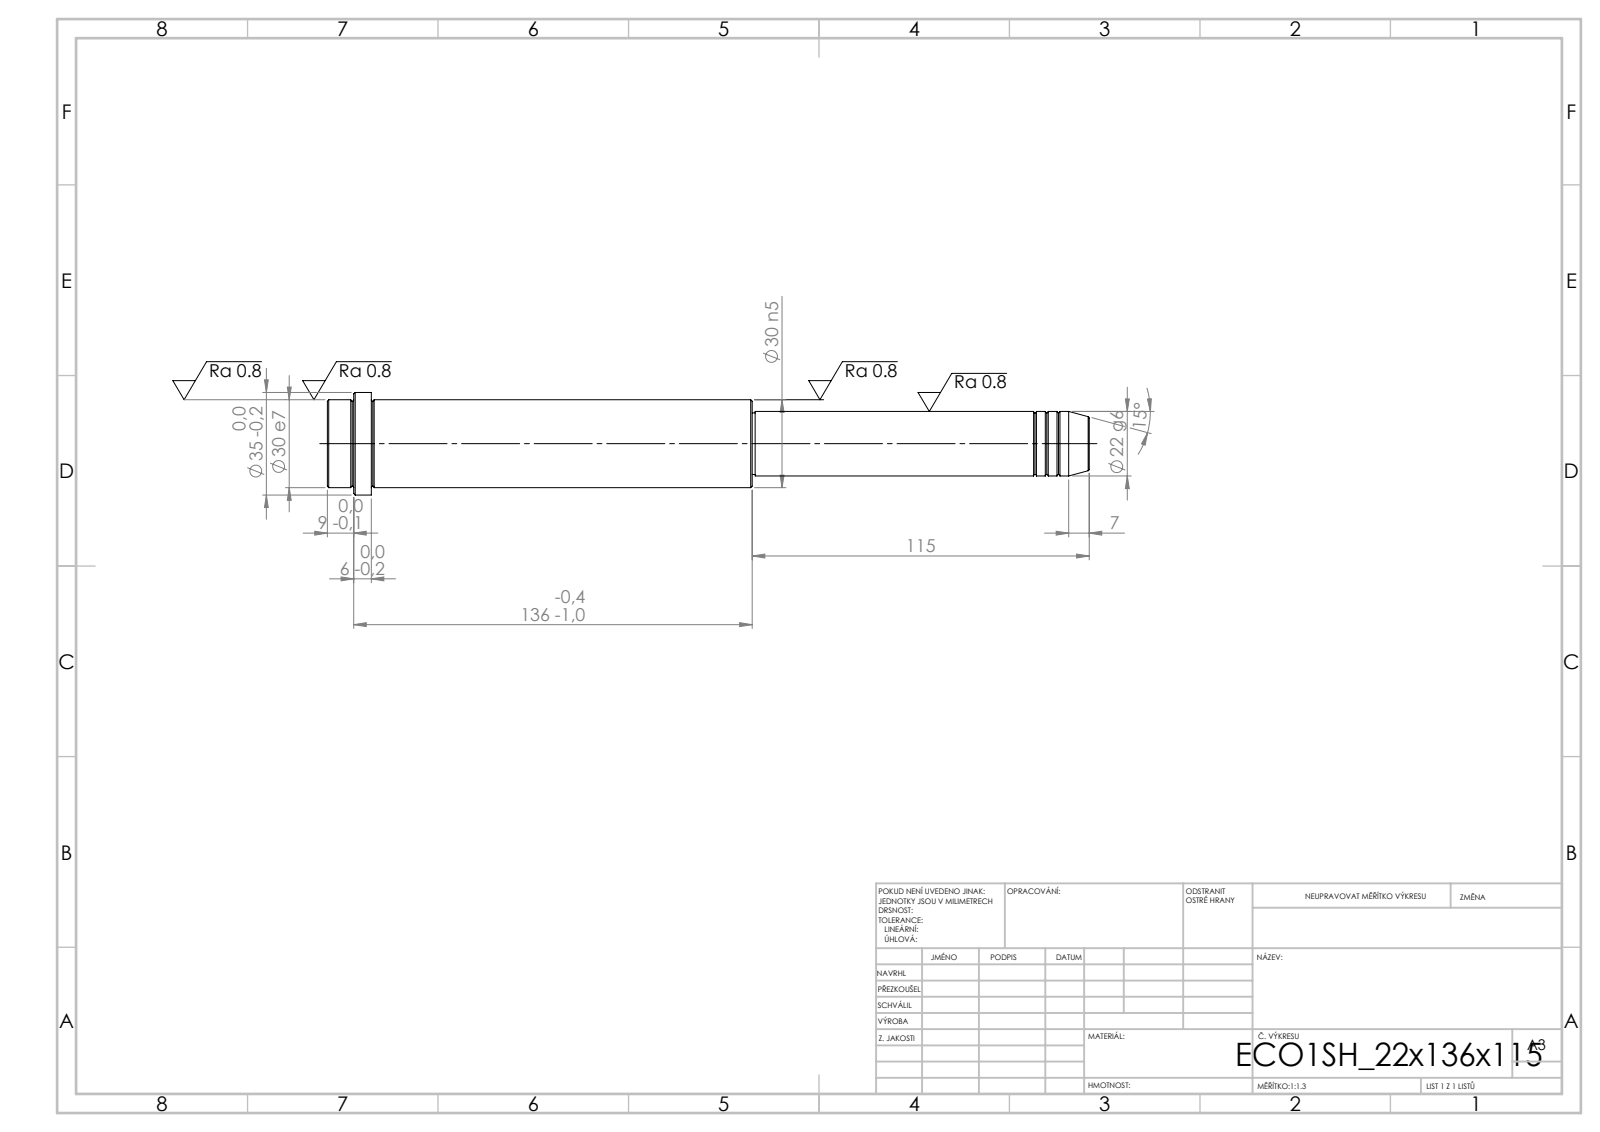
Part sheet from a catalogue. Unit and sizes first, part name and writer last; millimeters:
Units: millimetres
Overall size (bounding box): 260 × 35 × 35
Round bosses / shafts (diameter × count): ⌀35 ×1, ⌀30 ×1, ⌀22 ×1, ⌀21 ×1
Main face-to-face distances: 145, 130, 15, 115, 245, 260, 251, 136, 6, 9
Volume: 147 088 mm³ · Surface area: 23 668 mm²
Bodies: 1 solid, 52 faces (6 planar, 16 cylindrical, 30 other)
STEP written by: SolidWorks 2019 (CONFIG_CONTROL_DESIGN)
